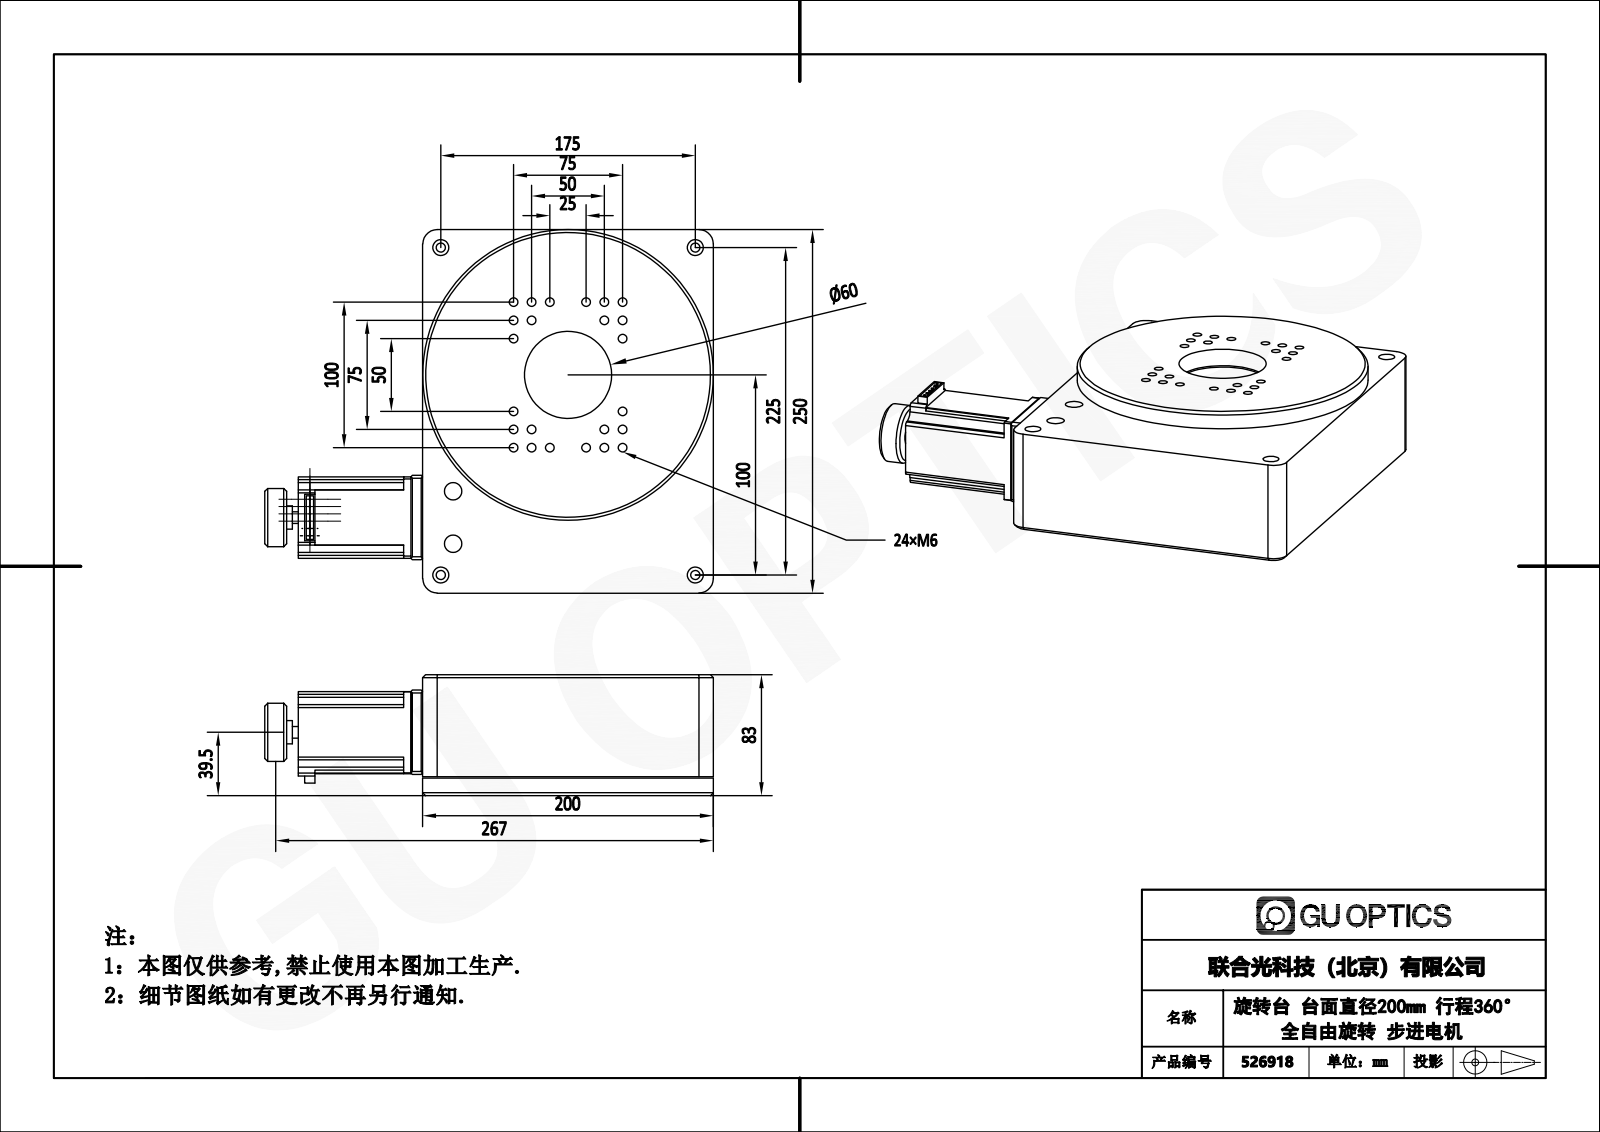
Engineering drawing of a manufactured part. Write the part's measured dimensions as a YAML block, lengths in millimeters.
part_name: "FMSR200H"
step_written_by: "SolidWorks 2017 (AUTOMOTIVE_DESIGN)"
units: millimeters
bodies: {solids: 4, faces: 271, planar: 107, cylindrical: 138, other: 26}
overall_size: [308.5, 250, 83]
volume: 3868000
surface_area: 282185
round_holes:
  - {diameter: 6, count: 24}
  - {diameter: 5, count: 4}
  - {diameter: 5.1, count: 4}
  - {diameter: 6.5, count: 4}
  - {diameter: 11, count: 4}
  - {diameter: 12, count: 2}
  - {diameter: 24, count: 1}
  - {diameter: 39, count: 1}
  - {diameter: 60, count: 1}
round_bosses_or_shafts:
  - {diameter: 1, count: 6}
  - {diameter: 200, count: 1}
  - {diameter: 40, count: 1}
  - {diameter: 38, count: 1}
  - {diameter: 16, count: 1}
  - {diameter: 8, count: 1}
  - {diameter: 6.35, count: 1}
partial_cylinders:
  - {radius: 2, count: 14}
  - {radius: 5, count: 4}
  - {radius: 10, count: 4}
face_to_face_distances: [70, 1, 71, 13, 83, 12, 200, 250, 8, 208]
hole_center_spacings: [12.5, 100.78, 62.5, 17.68, 88.39, 63.74, 76.03, 51.54]
